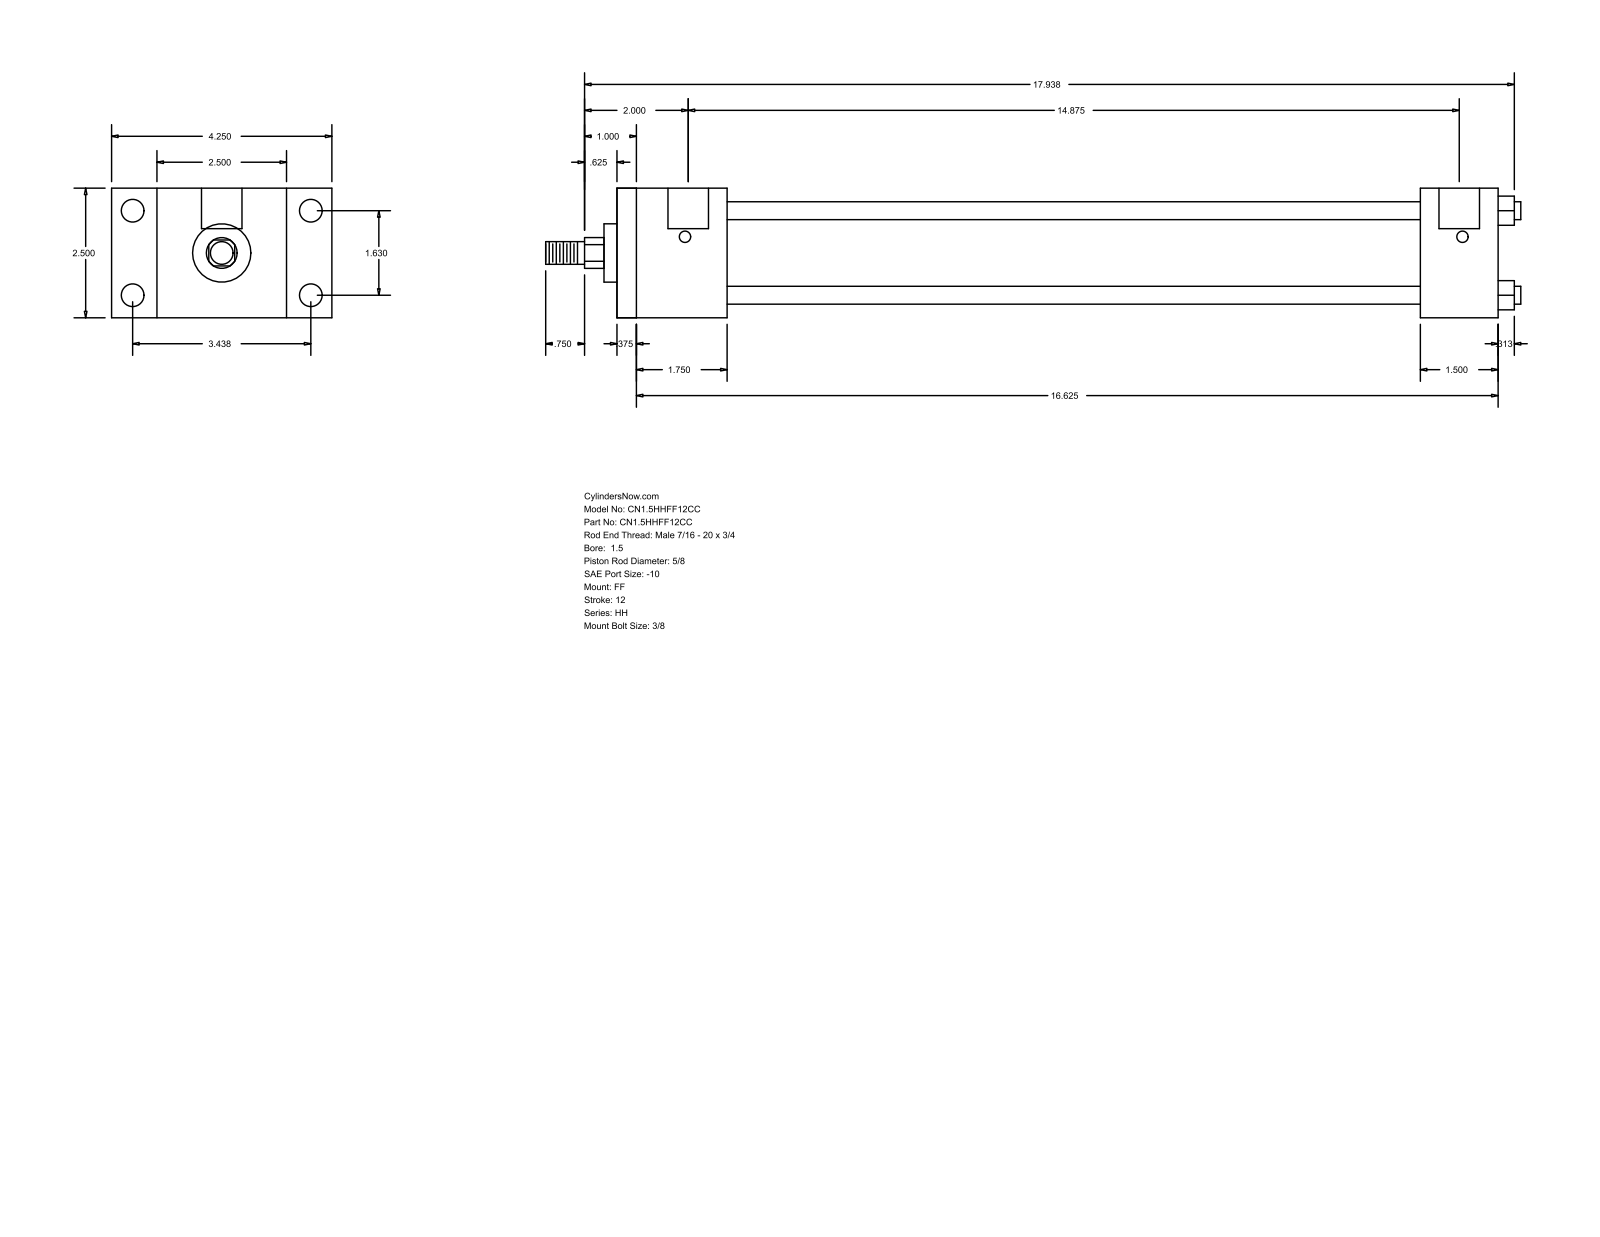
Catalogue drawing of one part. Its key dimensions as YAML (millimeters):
part_name: "HH_FF__0150_0.625"
step_written_by: "GSSL Pune (CONFIG_CONTROL_DESIGN)"
units: millimeters
bodies: {solids: 0, faces: 92, planar: 64, cylindrical: 28, other: 0}
overall_size: [477.84, 107.95, 63.5]
round_holes:
  - {diameter: 5.56, count: 4}
  - {diameter: 11.13, count: 4}
  - {diameter: 19.84, count: 2}
round_bosses_or_shafts:
  - {diameter: 8.76, count: 4}
  - {diameter: 44.45, count: 1}
  - {diameter: 28.57, count: 1}
  - {diameter: 15.88, count: 1}
  - {diameter: 11.11, count: 1}
partial_cylinders:
  - {radius: 7.54, count: 1}
face_to_face_distances: [63.5, 431.8, 9.52, 422.28, 44.45, 53.97, 377.83, 393.69, 384.17, 339.72]
hole_center_spacings: [1.59, 41.4, 87.32, 96.64, 379.41, 381, 377.82]
